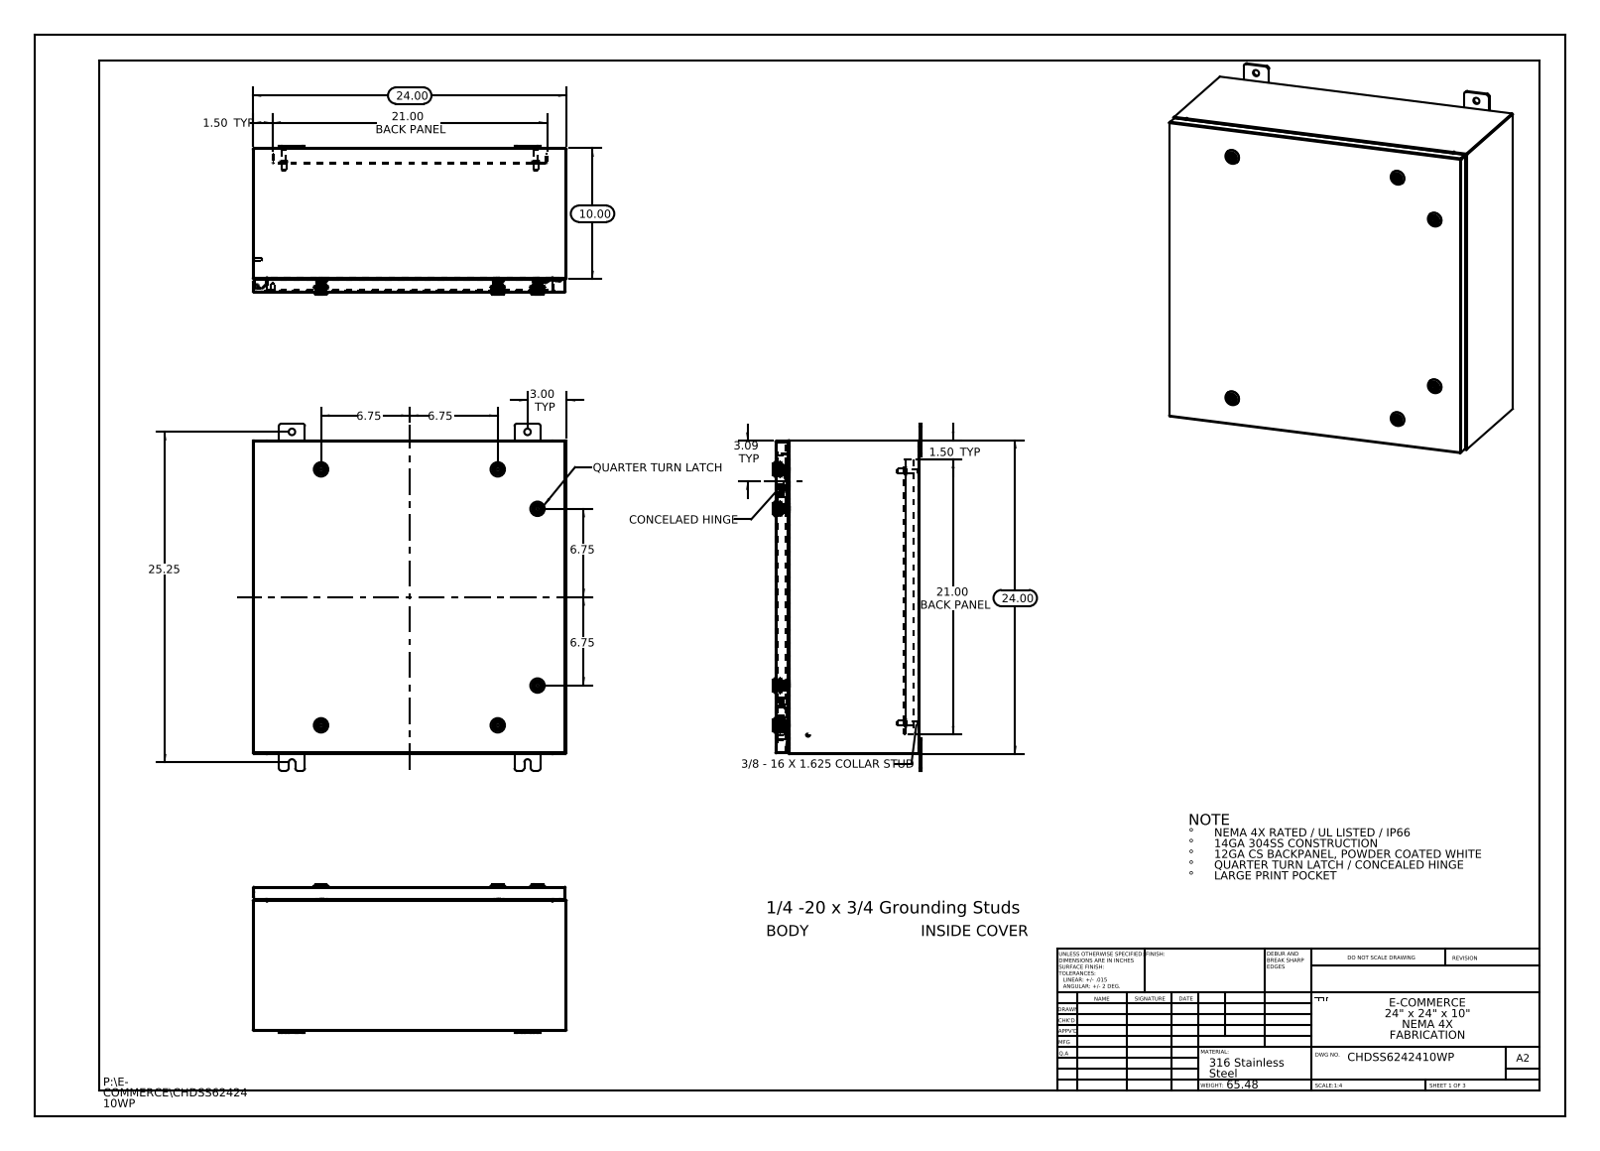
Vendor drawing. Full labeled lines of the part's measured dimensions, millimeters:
Part name (STEP PRODUCT): Housing-211301-IB-Industrilas_Housing-211301-IB-Industrilas; Washer-221320-IB-Industrilas_Washer-221320-IB-Industrilas; Nut-211301-IB-Industrilas_Nut-211301-IB-Industrilas; HW-CLH-R001-0500_2412-026240-2445-Industrilas (+8 more)
STEP written by: SolidWorks 2013 (CONFIG_CONTROL_DESIGN)
Units: millimetres
Bodies: 55 solids, 5420 faces (1592 planar, 1692 cylindrical, 2136 other)
Overall size (bounding box): 673.1 × 609.6 × 288.4
Volume: 3 817 000 mm³ · Surface area: 3 765 000 mm²
Round holes (diameter × count): ⌀12.7 ×8, ⌀5 ×6, ⌀10 ×6, ⌀10.2 ×6, ⌀16 ×6, ⌀20 ×6, ⌀3.5 ×4, ⌀5.4 ×1
Round bosses / shafts (diameter × count): ⌀6 ×8, ⌀28 ×6, ⌀19.8 ×6, ⌀15.9 ×6, ⌀15.5 ×6, ⌀13.5 ×6, ⌀10 ×6, ⌀2.9 ×6
Partial cylindrical surfaces — rounded edges, fillets, slot ends (radius × count): R0.2 ×198, R3 ×198, R0.7 ×72, R0.5 ×24, R4.8 ×24, R5 ×24, R0.3 ×20, R2.2 ×18
Main face-to-face distances: 1.9, 607.7, 1.9, 279.7, 277.7, 277.8, 275.9, 605.8, 609.6, 2.6
Hole centre spacings: 342.9, 47.2, 73.1, 77.9, 416, 427.1, 457.2, 489
